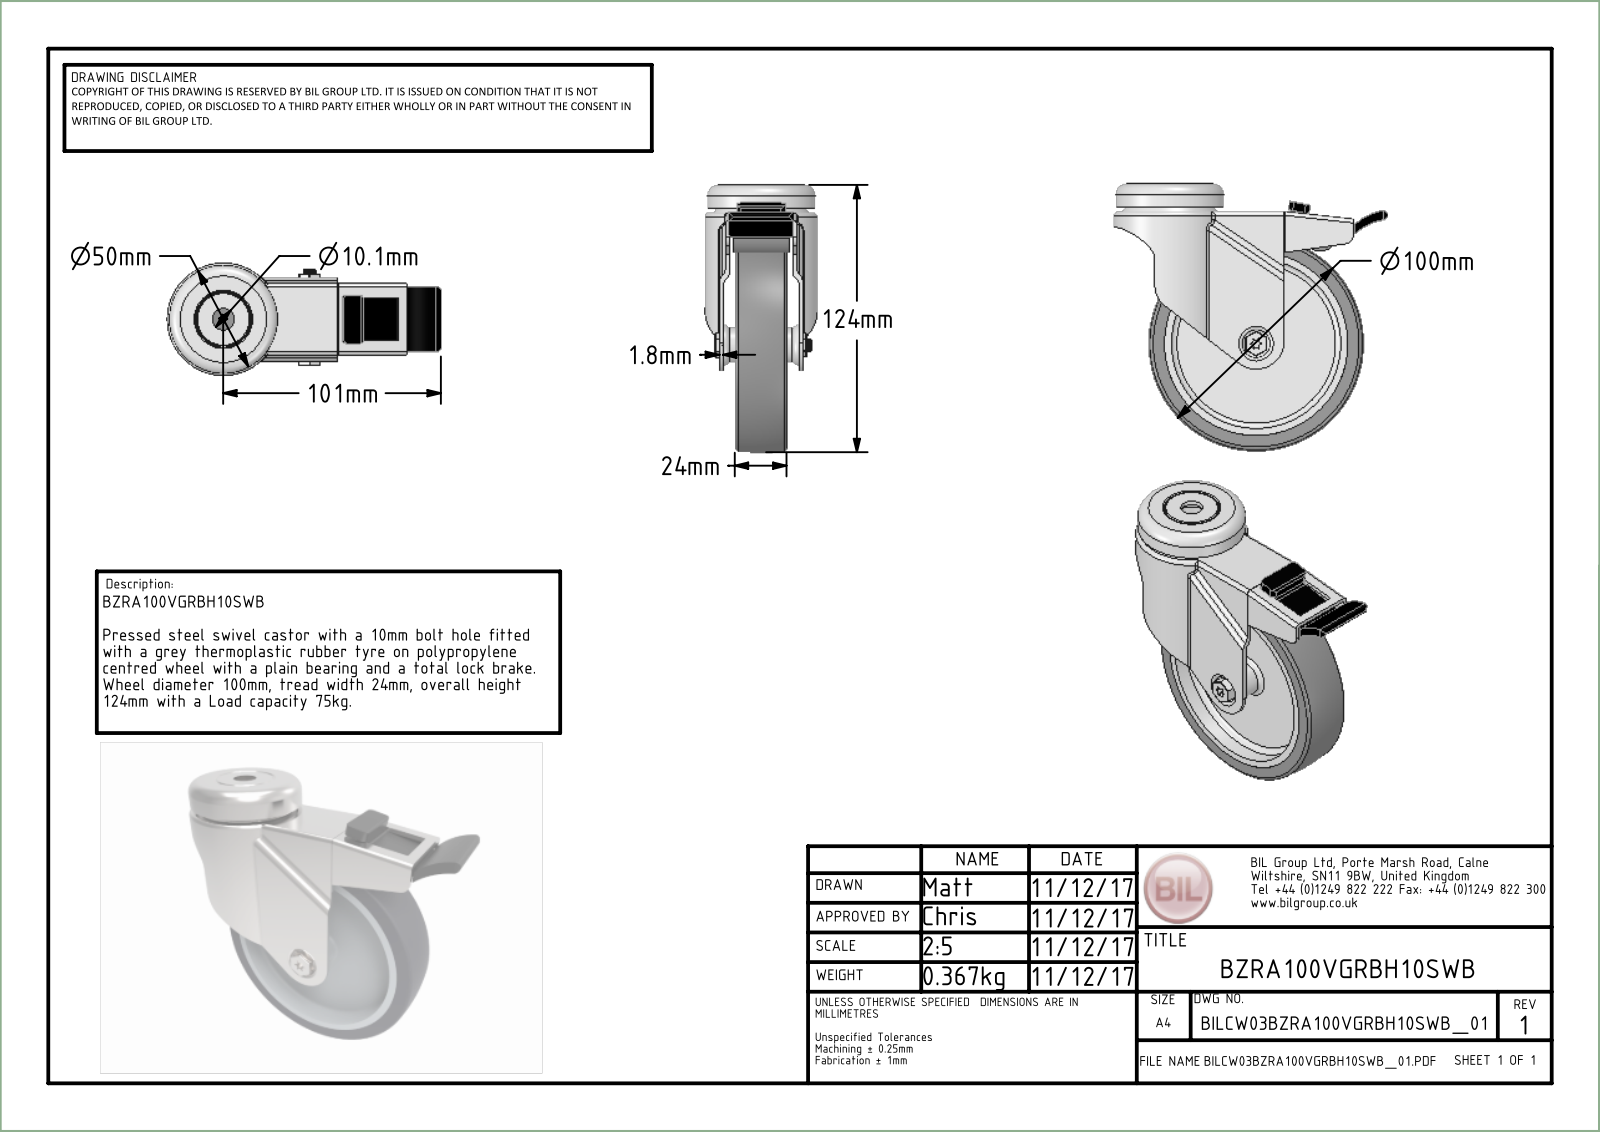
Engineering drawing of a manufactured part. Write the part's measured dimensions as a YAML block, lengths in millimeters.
part_name: "BZRA100VGRBH10SWB v3; BZRA100ASBH10SWB v1; ZINC PLATED PRESSED STEEL HEAD; ZINC PLATED PRESSED STEEL FORKS (+8 more)"
step_written_by: "Autodesk Translation Framework v13.20.0.188 (AP242_MANAGED_MODEL_BASED_3D_ENGINEERING_MIM_LF)"
units: millimeters
bodies: {solids: 10, faces: 473, planar: 201, cylindrical: 152, other: 120}
overall_size: [126, 124, 50]
volume: 148467
surface_area: 84298
round_holes:
  - {diameter: 6, count: 1}
  - {diameter: 6.3, count: 1}
  - {diameter: 6.4, count: 1}
  - {diameter: 8.2, count: 1}
  - {diameter: 8.3, count: 1}
  - {diameter: 10.5, count: 1}
  - {diameter: 10.56, count: 1}
  - {diameter: 30, count: 1}
  - {diameter: 82.75, count: 1}
round_bosses_or_shafts:
  - {diameter: 100, count: 1}
  - {diameter: 39, count: 1}
  - {diameter: 18, count: 1}
  - {diameter: 15, count: 1}
  - {diameter: 14.76, count: 1}
  - {diameter: 8, count: 1}
  - {diameter: 7.95, count: 1}
  - {diameter: 5.88, count: 1}
partial_cylinders:
  - {radius: 1.8, count: 27}
  - {radius: 1, count: 22}
  - {radius: 0.5, count: 13}
  - {radius: 1.5, count: 12}
  - {radius: 0.4, count: 6}
  - {radius: 0.9, count: 4}
  - {radius: 2, count: 4}
  - {radius: 5, count: 2}
face_to_face_distances: [1.8, 33.8, 6, 3, 11.5, 4.8, 9, 31.3, 2.5, 15]
